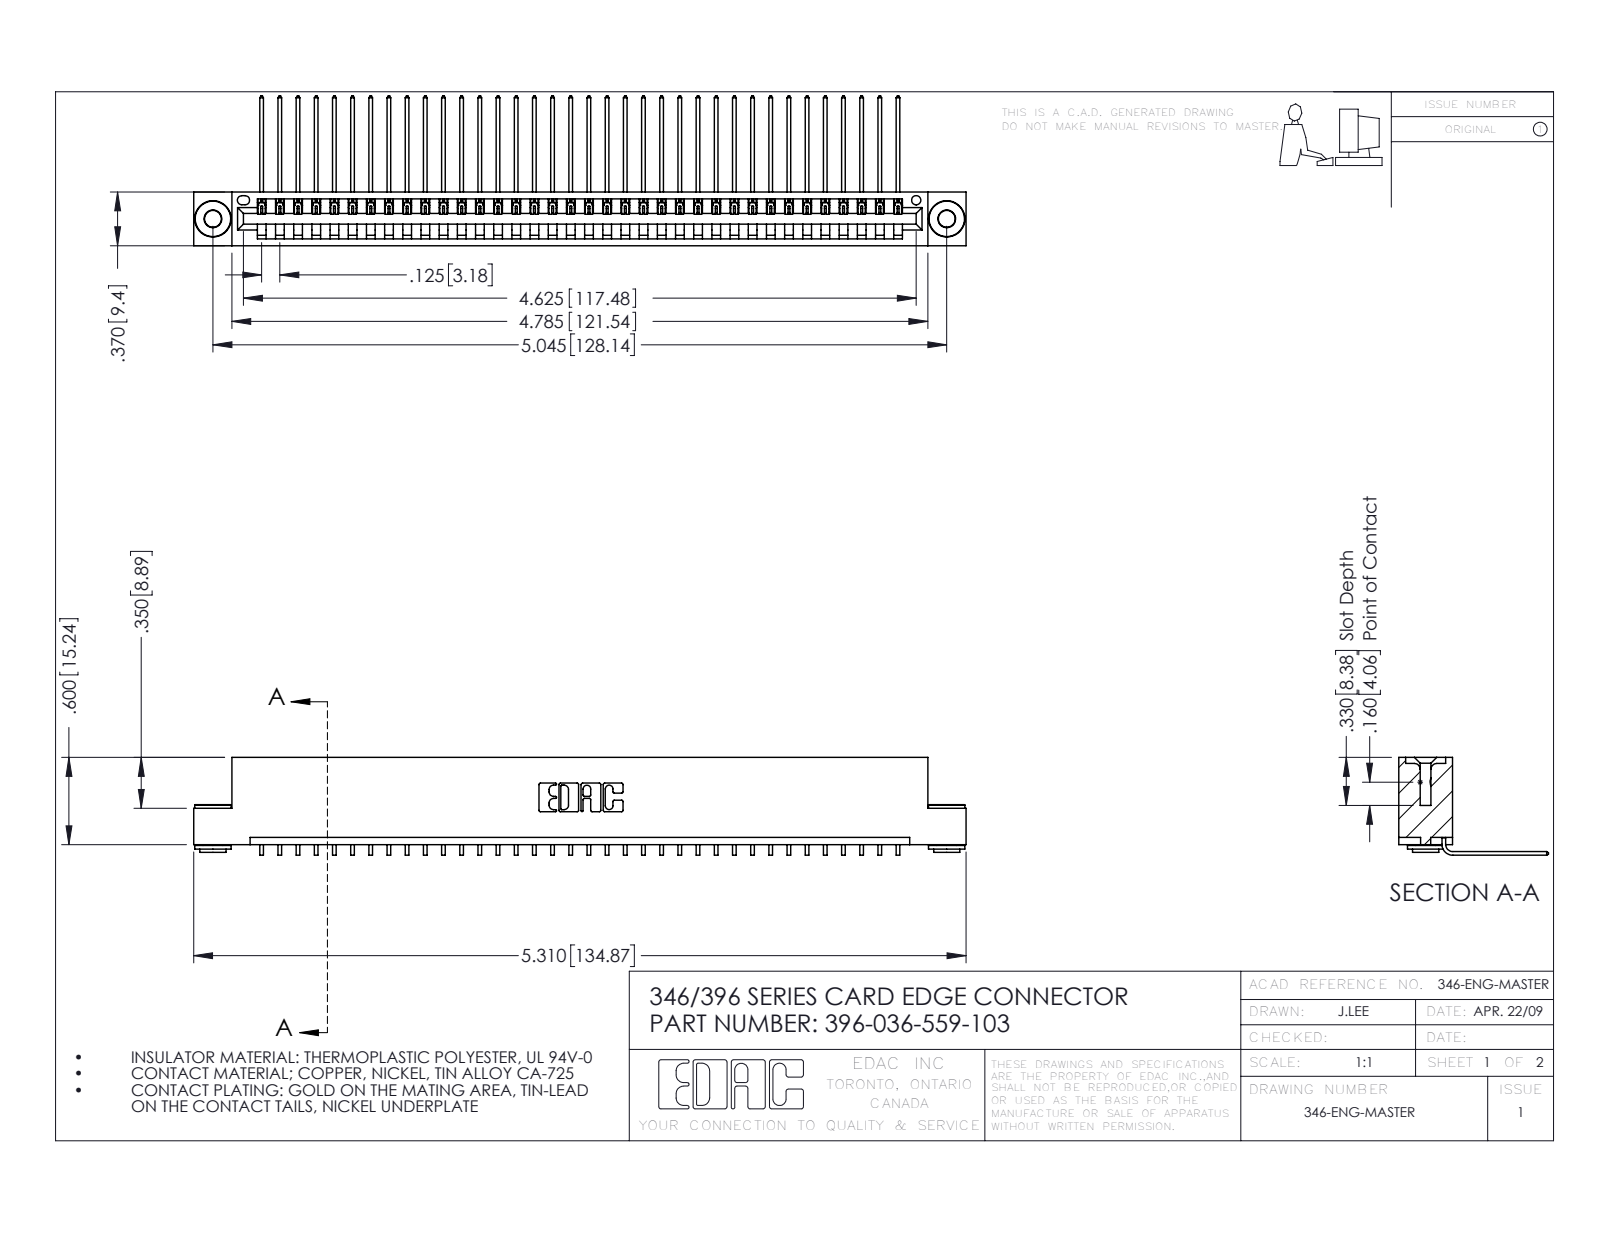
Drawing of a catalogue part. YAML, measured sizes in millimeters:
part_name: "346 Part_Flush Mounting Lugs - 0.156 Dia-TH; 345-292-001_558 559 Tail - 1; 345-250-002_345-250-002-102; 396-036-559-103"
step_written_by: "SolidWorks 2016 (CONFIG_CONTROL_DESIGN)"
units: millimeters
bodies: {solids: 39, faces: 2320, planar: 1598, cylindrical: 714, other: 8}
overall_size: [134.9, 26.2, 17.1]
volume: 13000
surface_area: 17130
round_holes:
  - {diameter: 2.9, count: 2}
  - {diameter: 4, count: 2}
  - {diameter: 1.6, count: 1}
round_bosses_or_shafts:
  - {diameter: 6.4, count: 2}
  - {diameter: 4.6, count: 2}
  - {diameter: 3.5, count: 2}
partial_cylinders:
  - {radius: 0.2, count: 72}
  - {radius: 0.3, count: 22}
  - {radius: 0.2, count: 6}
  - {radius: 0.8, count: 6}
  - {radius: 0.7, count: 3}
  - {radius: 0.8, count: 2}
  - {radius: 1, count: 2}
  - {radius: 0.4, count: 1}
face_to_face_distances: [1.2, 8.2, 9.4, 6.4, 0.6, 1.8, 7.6, 3.8, 5.6, 2.5]
hole_center_spacings: [6.2, 122.8, 128.1]
